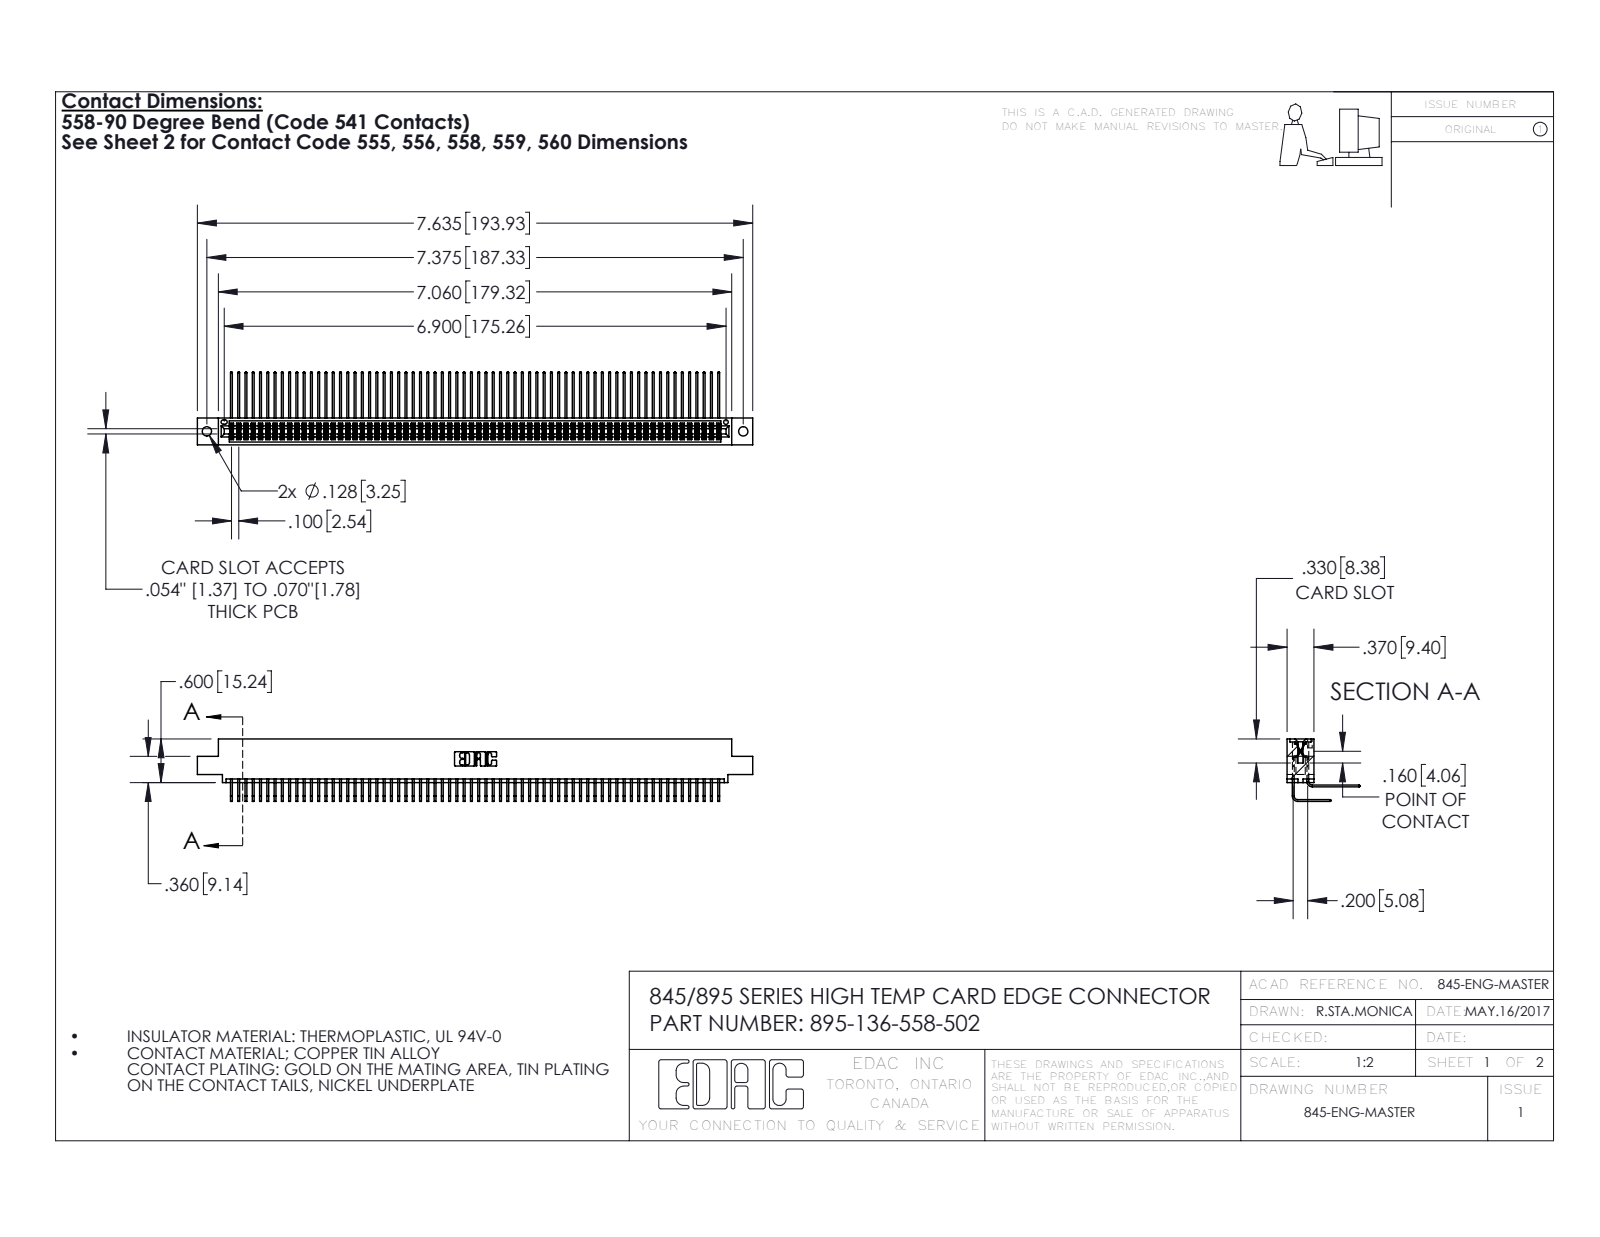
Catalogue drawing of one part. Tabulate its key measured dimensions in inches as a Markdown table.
| quantity | value |
| --- | --- |
| part name | 395-136-558-502; 345 Part_0.110 Offset - 0.128 Dia; 345-292-001_558 Tail - 2; 345-292-001_558 559 Tail - 1 |
| STEP written by | SolidWorks 2016 (CONFIG_CONTROL_DESIGN) |
| units | inches |
| bodies | 137 solids, 7202 faces (4844 planar, 2358 cylindrical, 0 other) |
| overall size | 7.635 × 1.005 × 0.859 |
| volume | 1.205 in³ |
| surface area | 51.48 in² |
| round holes (diameter × count) | 0.128 × 2, 0.064 × 1 |
| partial cylindrical surfaces (radius × count) | 0.006 × 205, 0.01 × 22, 0.007 × 6, 0.031 × 6, 0.026 × 3, 0.014 × 2, 0.019 × 2, 0.022 × 2 |
| main face-to-face distances | 0.072, 0.298, 0.2, 0.37, 0.098, 0.272, 0.025, 0.225, 0.025, 0.175 |
| hole center spacings | 0.27, 7.139, 7.375 |
